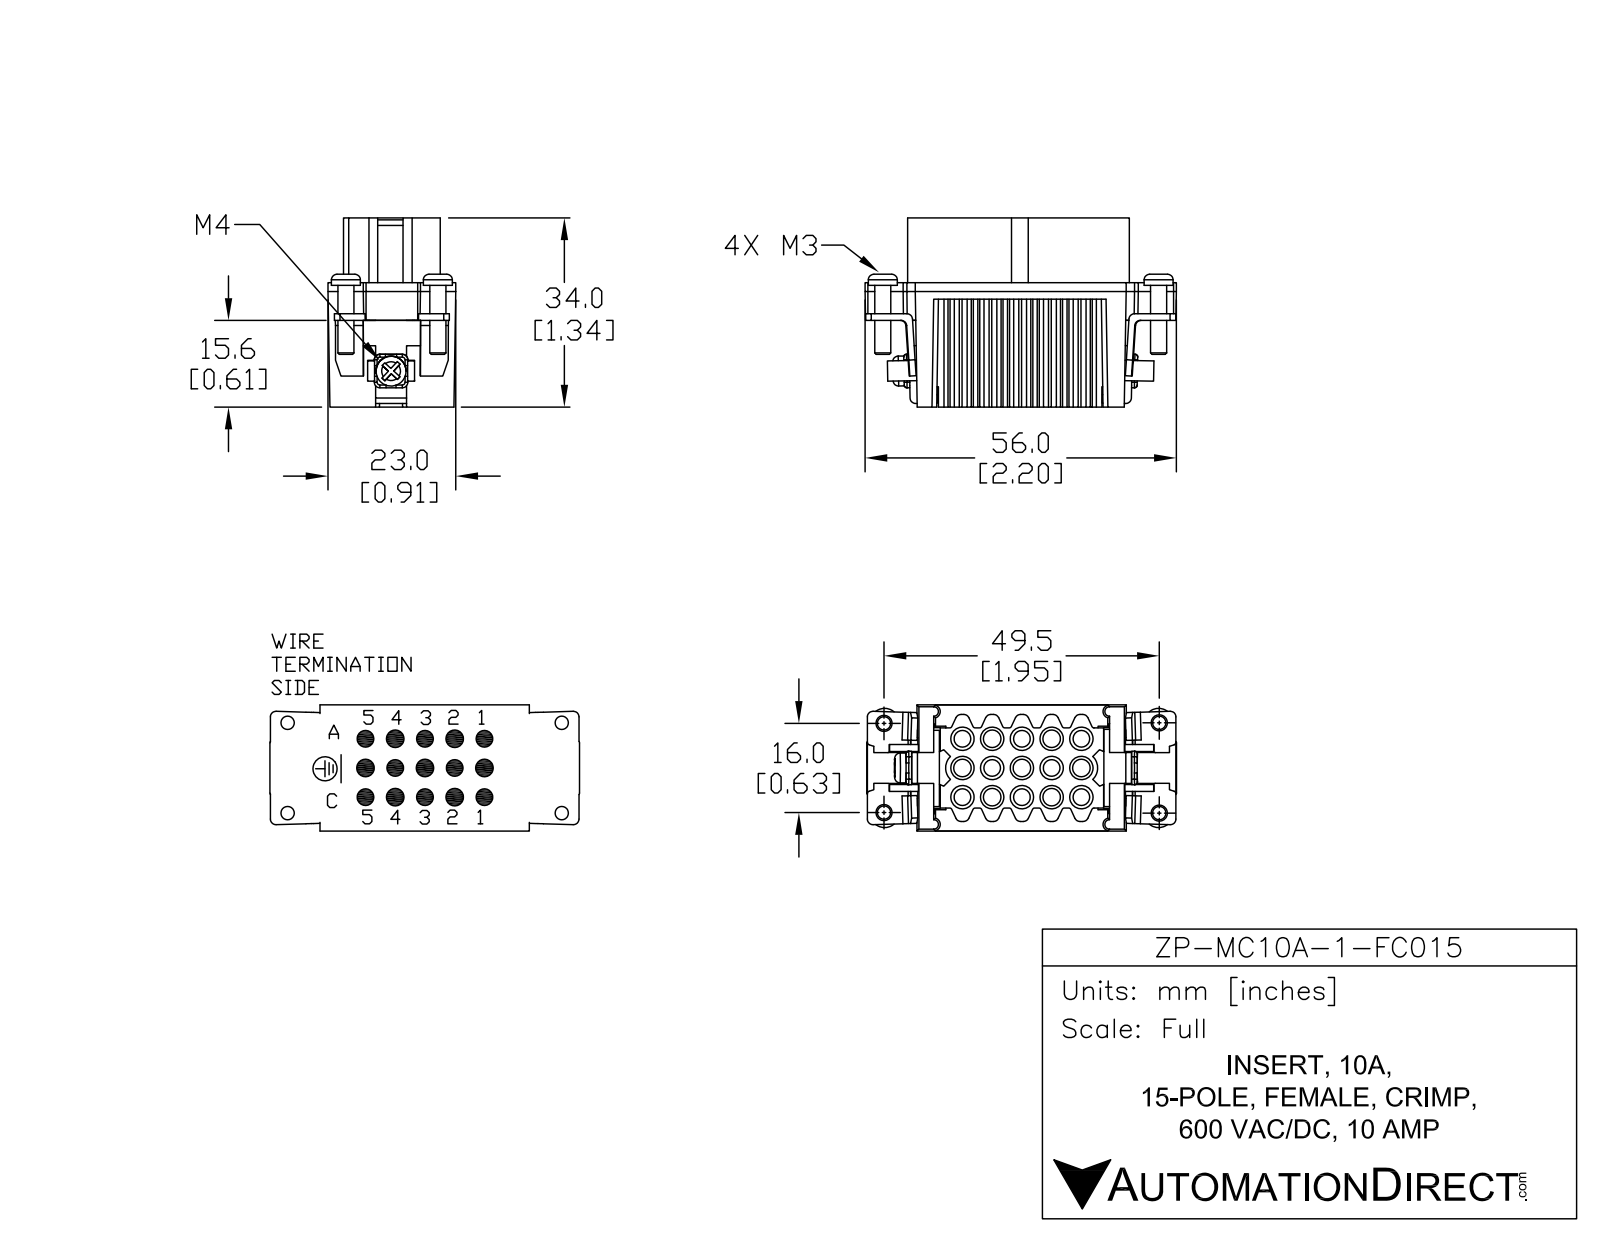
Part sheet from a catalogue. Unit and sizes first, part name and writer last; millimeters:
Units: millimetres
Overall size (bounding box): 56 × 34.1 × 23
Round holes (diameter × count): ⌀3.2 ×15, ⌀5.6 ×7, ⌀2.5 ×4, ⌀2.7 ×4, ⌀3.3 ×1
Round bosses / shafts (diameter × count): ⌀5.4 ×4, ⌀5.2 ×4, ⌀3 ×4, ⌀2.3 ×4, ⌀7 ×1, ⌀5 ×1
Partial cylindrical surfaces — rounded edges, fillets, slot ends (radius × count): R0.5 ×74, R1.5 ×34, R0.2 ×24, R0.3 ×22, R1 ×12, R0.8 ×6, R0.7 ×4, R0.9 ×4
Main face-to-face distances: 1, 2.4, 3.4, 15.6, 34, 16.6, 19, 2.1, 1.4, 0.7
Hole centre spacings: 5.3, 11.9, 7.5, 10.6, 16.8, 15, 15.9, 14.4
Volume: 17 240 mm³ · Surface area: 14 750 mm²
Bodies: 1 solid, 1413 faces (736 planar, 329 cylindrical, 348 other)
Part name (STEP PRODUCT): ZP-MC10A-1-FC015
STEP written by: SolidWorks 2019 (AUTOMOTIVE_DESIGN)
